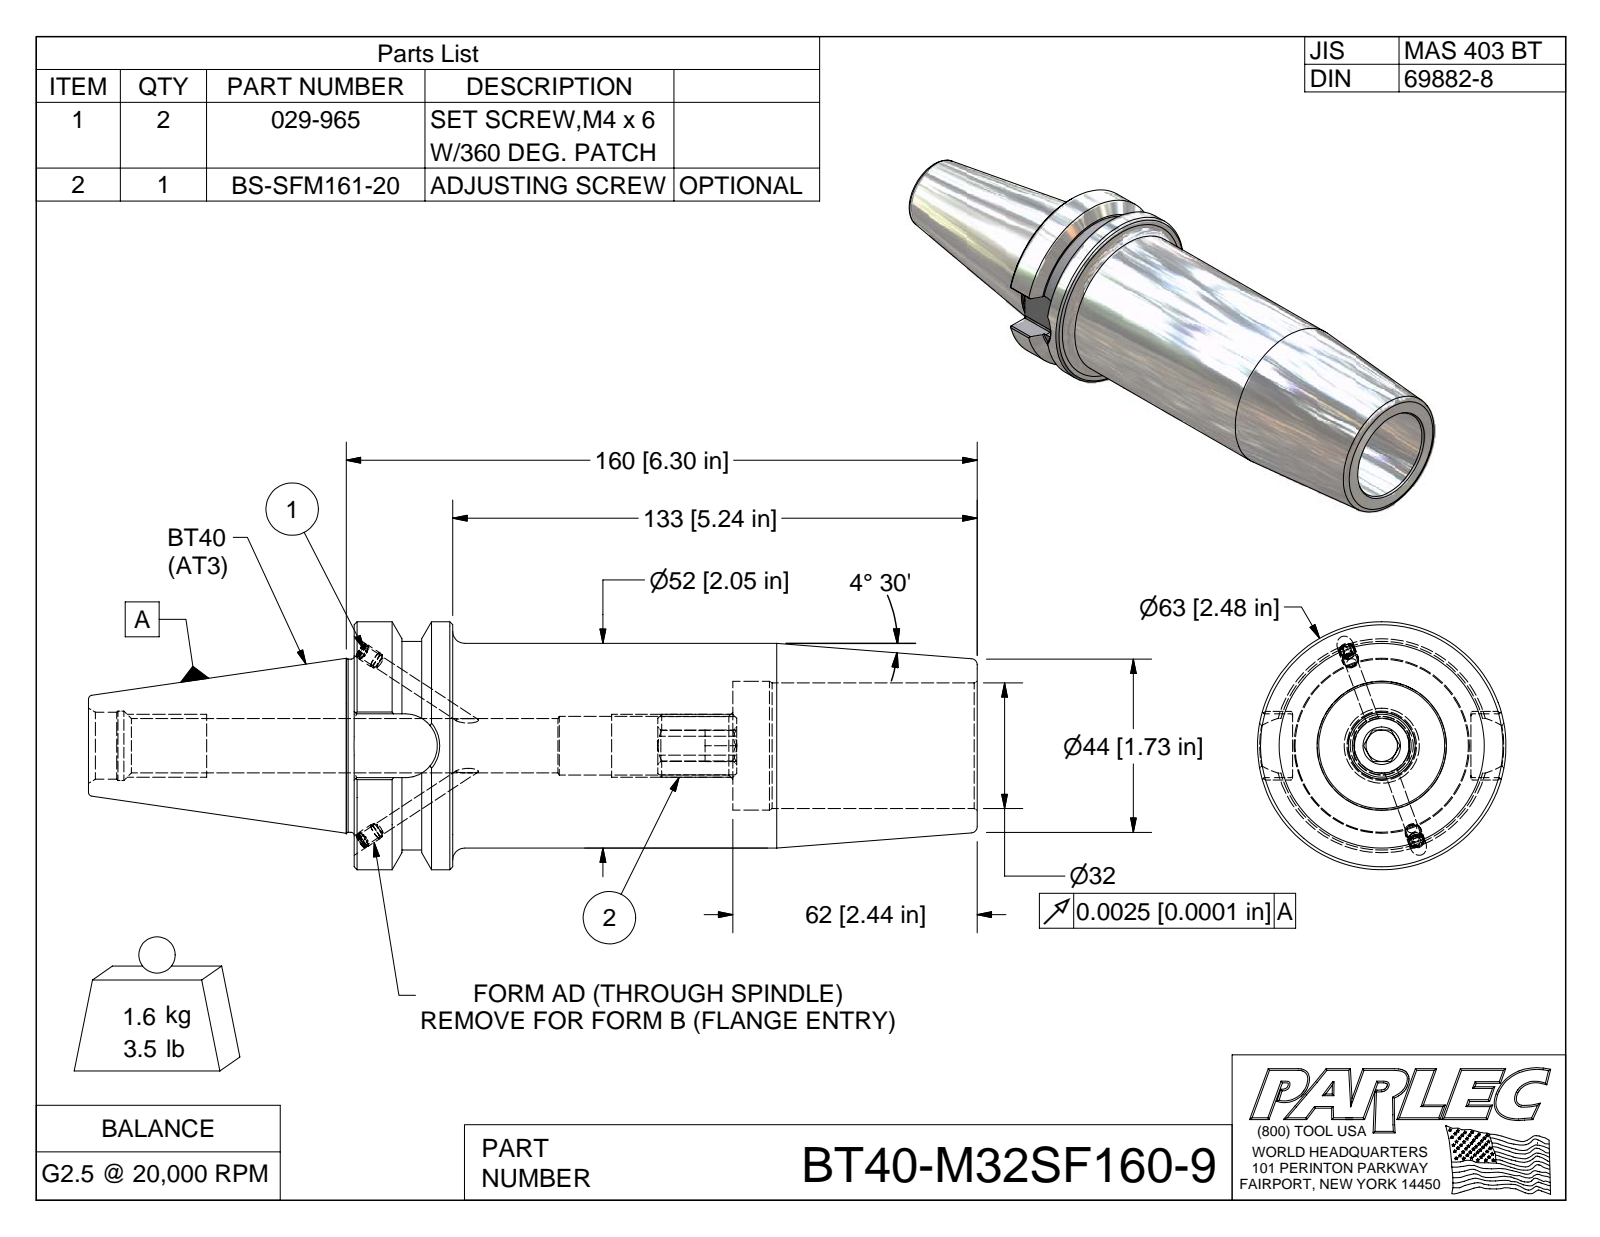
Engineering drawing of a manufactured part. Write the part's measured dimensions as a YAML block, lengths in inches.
part_name: "BT40-M32SF160-9; BT40BC-M32SF160-9-1; 029-965; BS-SFM161-20"
step_written_by: "Autodesk Inventor 2009 (AUTOMOTIVE_DESIGN)"
units: inches
bodies: {solids: 4, faces: 131, planar: 57, cylindrical: 33, other: 41}
overall_size: [8.874, 2.48, 2.48]
volume: 19.94
surface_area: 84.64
round_holes:
  - {diameter: 0.13, count: 2}
  - {diameter: 0.161, count: 2}
  - {diameter: 0.694, count: 1}
  - {diameter: 1.258, count: 1}
  - {diameter: 1.288, count: 1}
round_bosses_or_shafts:
  - {diameter: 0.165, count: 2}
  - {diameter: 0.157, count: 2}
  - {diameter: 2.48, count: 1}
  - {diameter: 2.087, count: 1}
  - {diameter: 2.047, count: 1}
  - {diameter: 1.75, count: 1}
  - {diameter: 1.73, count: 1}
partial_cylinders:
  - {radius: 0.02, count: 8}
  - {radius: 0.315, count: 1}
  - {radius: 0.319, count: 1}
face_to_face_distances: [3.78, 6.221, 2.441, 0.984, 2.796, 5.237, 0.615, 1.166, 1.78, 2.653]
